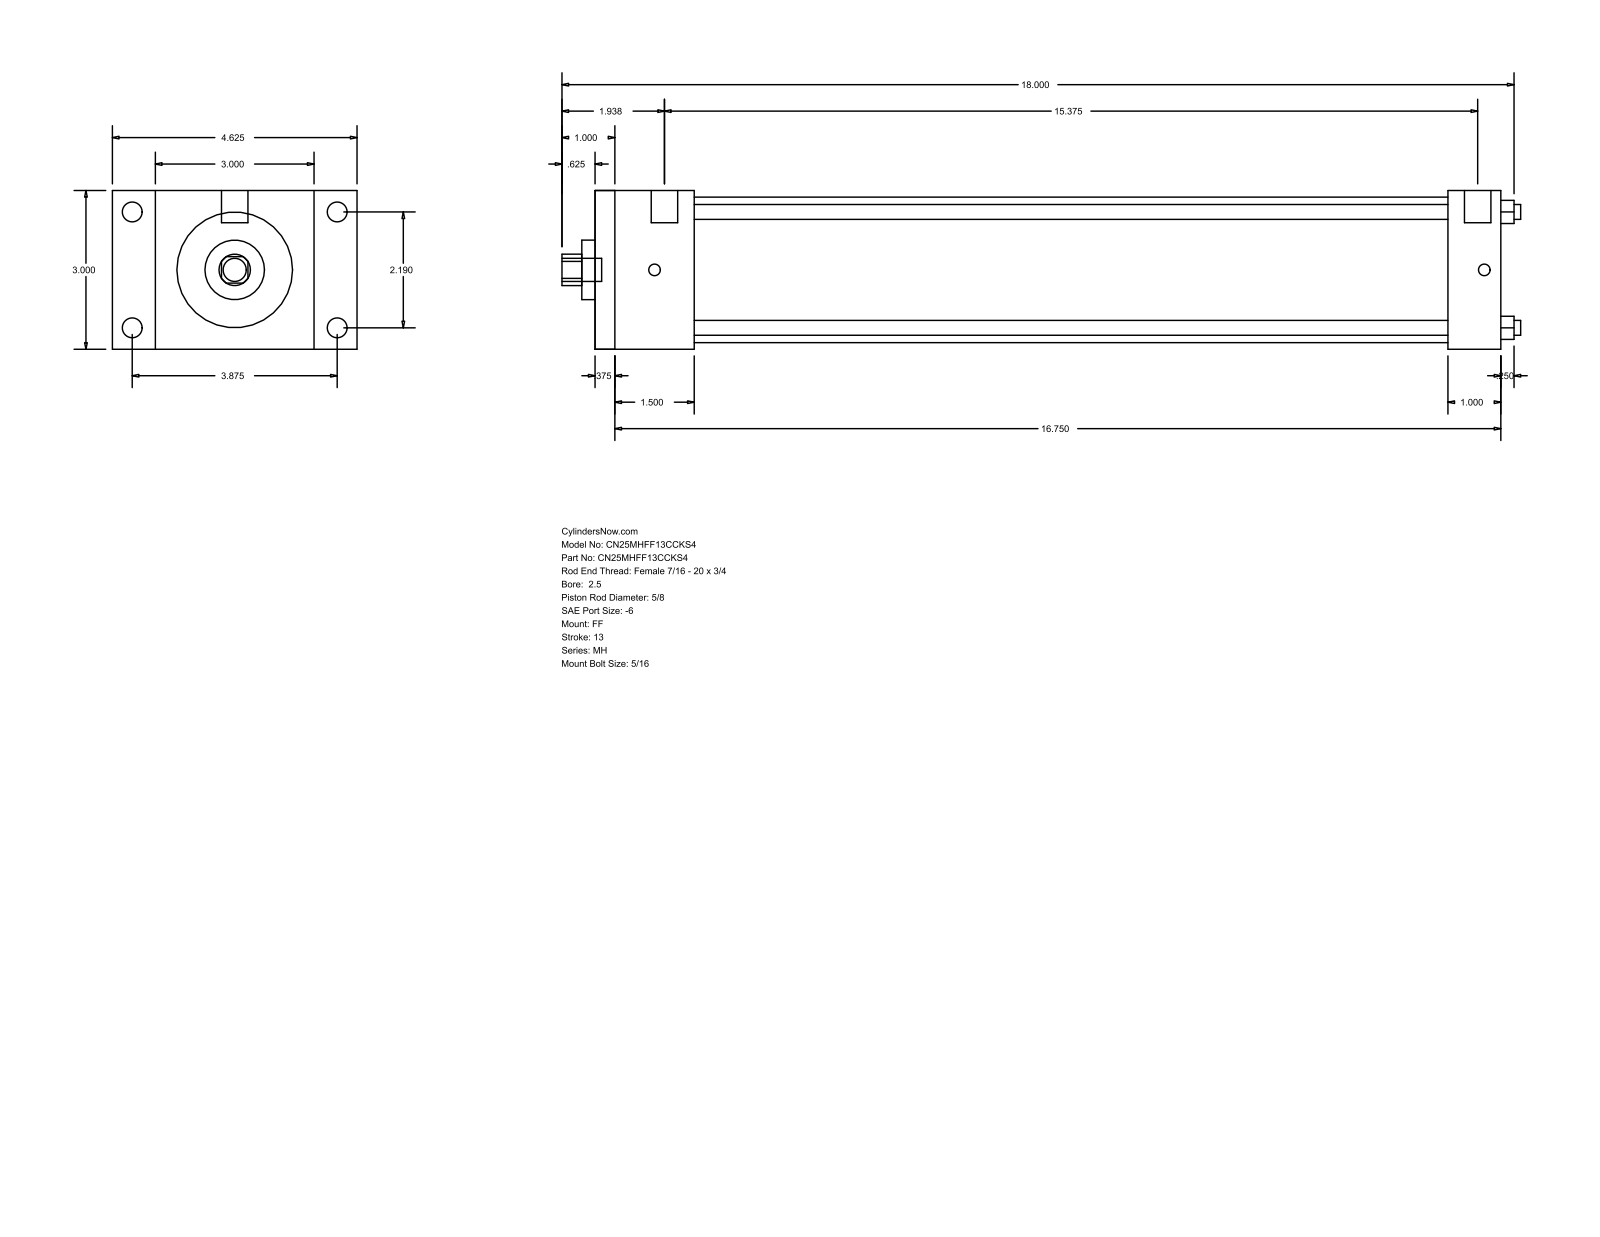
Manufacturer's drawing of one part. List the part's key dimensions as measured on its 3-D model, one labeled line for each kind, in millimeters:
Part name (STEP PRODUCT): MH_FF__0250_0.625
STEP written by: GSSL Pune (CONFIG_CONTROL_DESIGN)
Units: millimetres
Bodies: 0 solids, 92 faces (64 planar, 28 cylindrical, 0 other)
Overall size (bounding box): 460.38 × 117.47 × 76.2
Round holes (diameter × count): ⌀7.14 ×4, ⌀15.88 ×1, ⌀28.57 ×1, ⌀69.85 ×1
Round bosses / shafts (diameter × count): ⌀9.53 ×4, ⌀5.56 ×4, ⌀12.7 ×2, ⌀11.11 ×1
Partial cylindrical surfaces — rounded edges, fillets, slot ends (radius × count): R7.54 ×1
Main face-to-face distances: 76.2, 434.97, 9.52, 425.45, 25.4, 47.62, 409.57, 38.1, 400.05, 361.95
Hole centre spacings: 39.33, 55.62, 78.66
